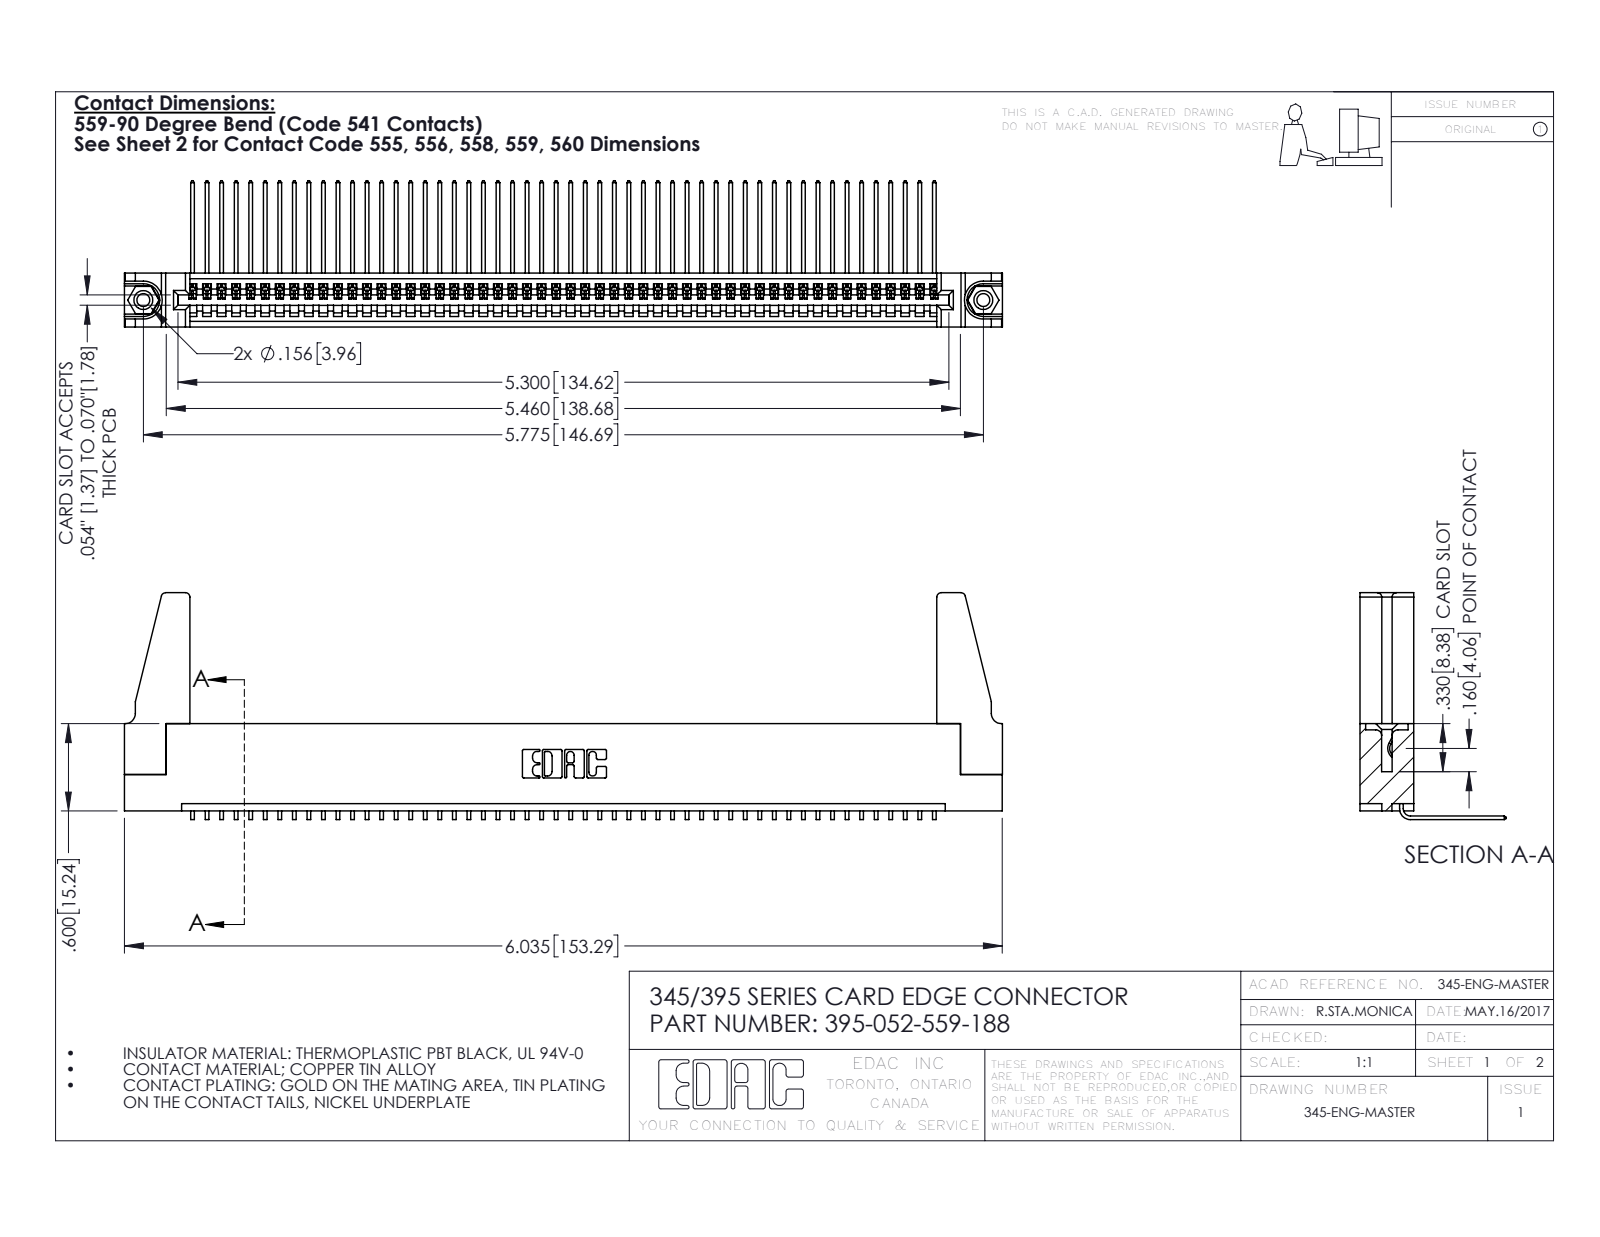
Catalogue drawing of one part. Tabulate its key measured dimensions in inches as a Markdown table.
| quantity | value |
| --- | --- |
| part name | 345-220-078_345-220-088; 345-250-001_345-250-001-102; 395-052-559-188; 345-292-001_558 559 Tail - 1 (+1 more) |
| STEP written by | SolidWorks 2016 (CONFIG_CONTROL_DESIGN) |
| units | inches |
| bodies | 57 solids, 3370 faces (2336 planar, 1018 cylindrical, 16 other) |
| overall size | 6.036 × 1.559 × 1.005 |
| volume | 1.103 in³ |
| surface area | 37.16 in² |
| round holes (diameter × count) | 0.089 × 2, 0.125 × 2, 0.156 × 2, 0.064 × 1 |
| round bosses / shafts (diameter × count) | 0.155 × 2 |
| partial cylindrical surfaces (radius × count) | 0.006 × 104, 0.01 × 22, 0.03 × 8, 0.007 × 6, 0.031 × 6, 0.026 × 3, 0.031 × 2, 0.04 × 2 |
| main face-to-face distances | 0.072, 0.298, 0.37, 0.2, 0.098, 0.272, 0.025, 0.225, 0.149, 0.072 |
| hole center spacings | 0.27, 5.539, 5.775 |
